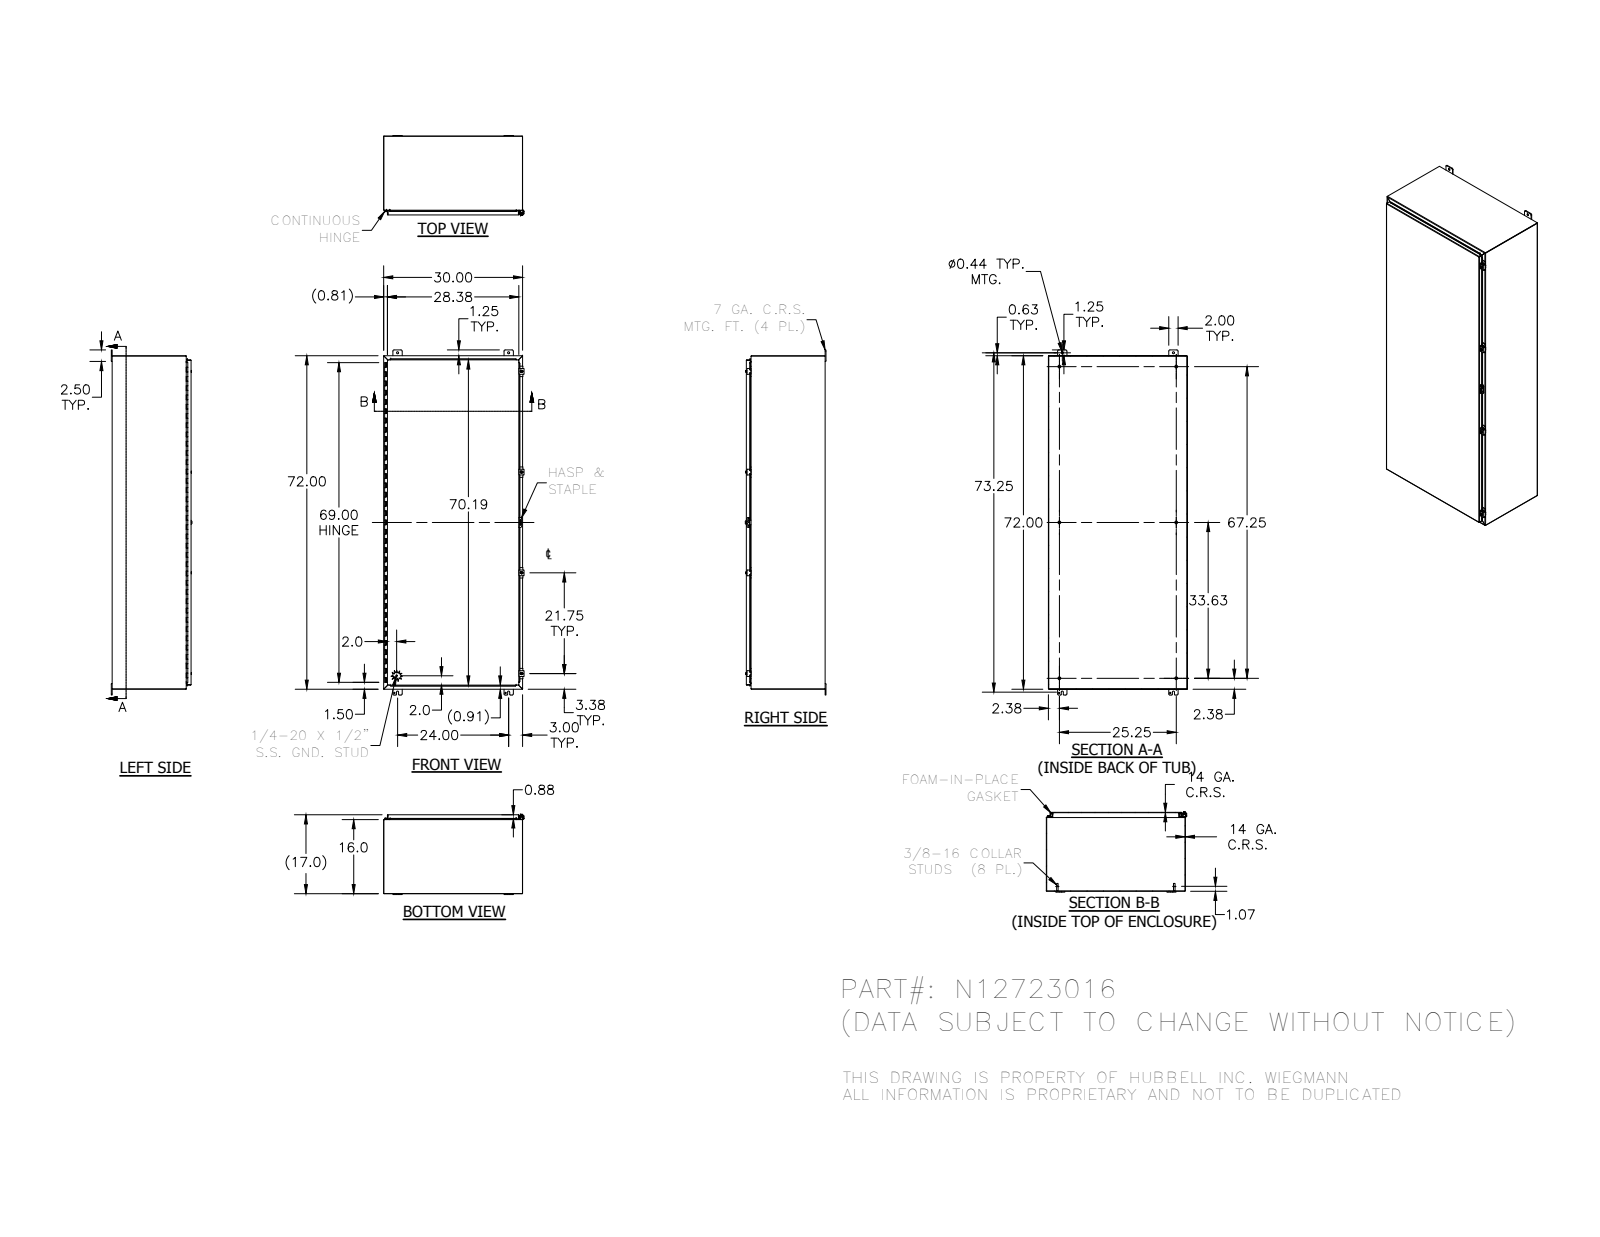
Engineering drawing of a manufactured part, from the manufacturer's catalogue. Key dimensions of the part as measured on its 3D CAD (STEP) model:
Part name (STEP PRODUCT): N12723016; 34840; 38413; N123016TB (+8 more)
STEP written by: Autodesk Inventor 2012 (AUTOMOTIVE_DESIGN)
Units: inches
Bodies: 41 solids, 1564 faces (927 planar, 496 cylindrical, 141 other)
Overall size (bounding box): 74.5 × 30.311 × 17.41
Volume: 629.4 in³ · Surface area: 16 749 in²
Round holes (diameter × count): ⌀0.211 ×4, ⌀0.281 ×4, ⌀0.3 ×4, ⌀0.313 ×4, ⌀0.438 ×4, ⌀0.11 ×3, ⌀0.125 ×1, ⌀0.156 ×1, ⌀0.5 ×1
Round bosses / shafts (diameter × count): ⌀0.625 ×6, ⌀0.33 ×6, ⌀0.25 ×6, ⌀0.52 ×4, ⌀0.5 ×4, ⌀0.35 ×4, ⌀0.337 ×1, ⌀0.12 ×1
Partial cylindrical surfaces — rounded edges, fillets, slot ends (radius × count): R0.03 ×51, R0.125 ×29, R0.25 ×29, R0.031 ×21, R0.105 ×21, R0.063 ×17, R0.1 ×8, R0.141 ×8
Main face-to-face distances: 0.074, 16.959, 29.926, 16.885, 17.033, 29.852, 30, 71.926, 15.926, 1.033
Hole centre spacings: 1.593, 24, 72, 75.894, 21.75, 0.791, 23.357, 24.729
